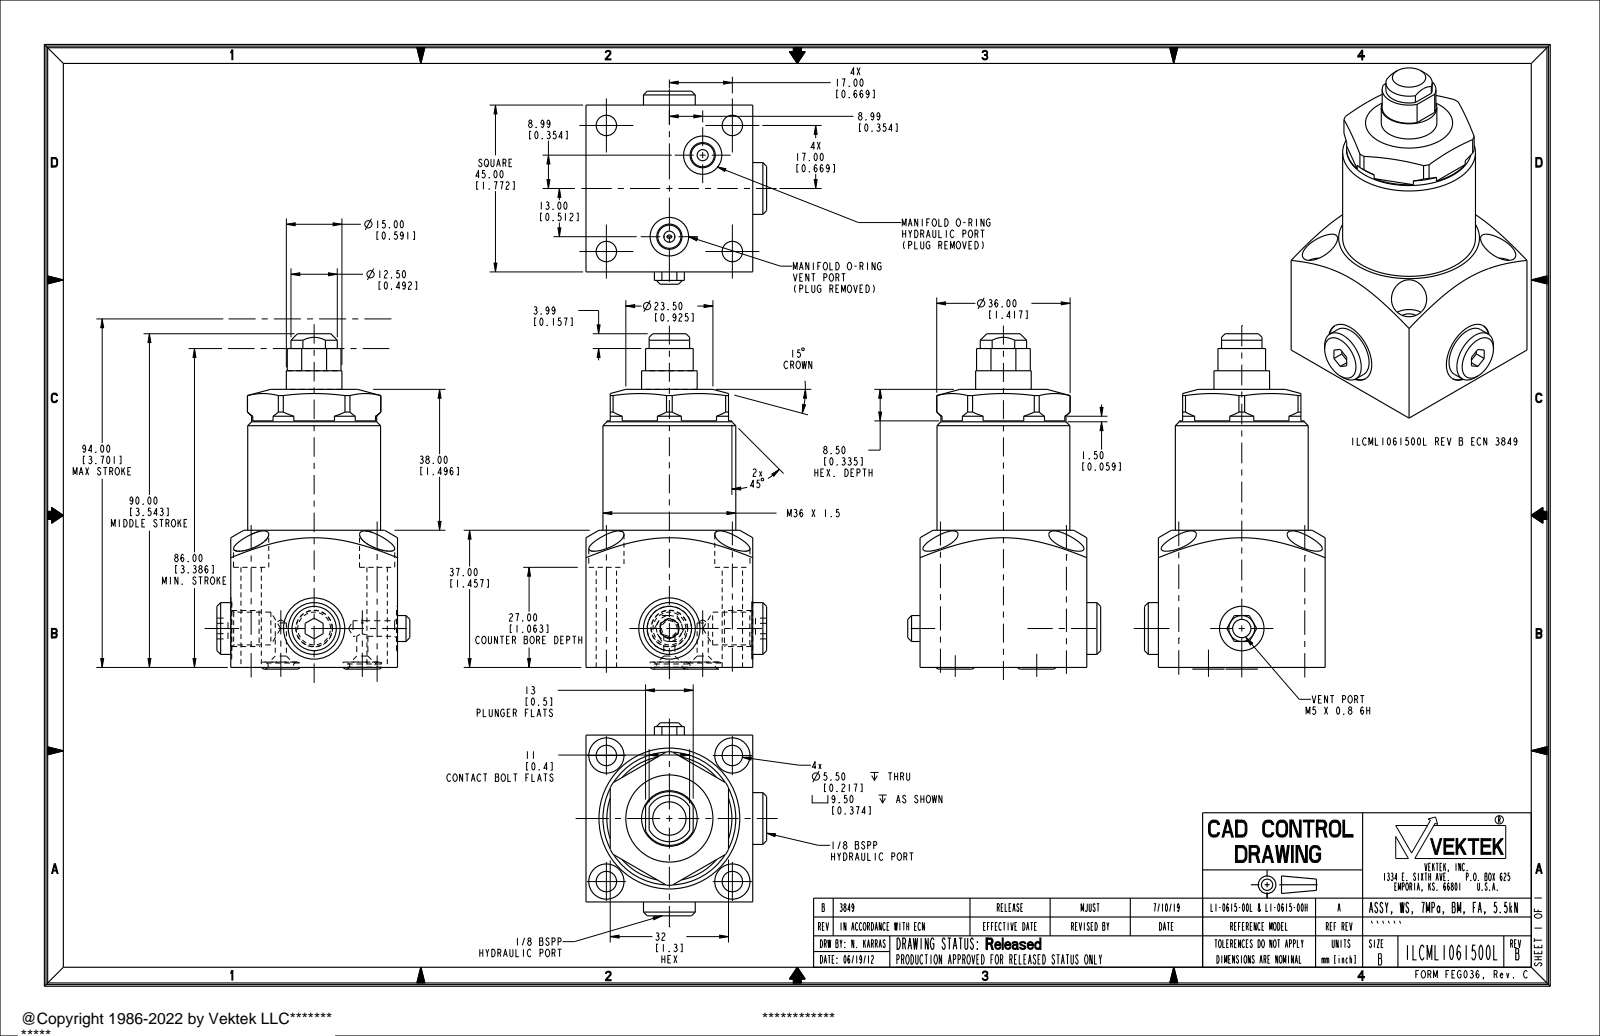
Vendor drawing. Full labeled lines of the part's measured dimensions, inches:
Part name (STEP PRODUCT): ILCML1061500L
STEP written by: PRO/ENGINEER BY PARAMETRIC TECHNOLOGY CORPORATION, 2017170 (AUTOMOTIVE_DESIGN)
Units: inches
Bodies: 1 solid, 179 faces (69 planar, 64 cylindrical, 46 other)
Overall size (bounding box): 3.561 × 2.05 × 1.919
Volume: 6.504 in³ · Surface area: 30.68 in²
Round holes (diameter × count): ⌀0.217 ×4, ⌀0.374 ×4, ⌀0.118 ×2, ⌀0.348 ×2, ⌀0.65 ×2, ⌀0.165 ×1, ⌀0.394 ×1, ⌀0.409 ×1, ⌀0.472 ×1
Round bosses / shafts (diameter × count): ⌀0.55 ×2, ⌀0.383 ×2, ⌀1.411 ×1, ⌀1.329 ×1, ⌀0.591 ×1
Partial cylindrical surfaces — rounded edges, fillets, slot ends (radius × count): R0.246 ×1, R0.285 ×1, R0.709 ×1
Main face-to-face distances: 1.772, 1.762, 1.257, 2.953, 0.257, 1.514, 1.063, 1.89, 1.919, 0.157
Hole centre spacings: 1.339, 0.687, 1.071, 1.357, 1.893, 0.446, 0.935, 1.447
